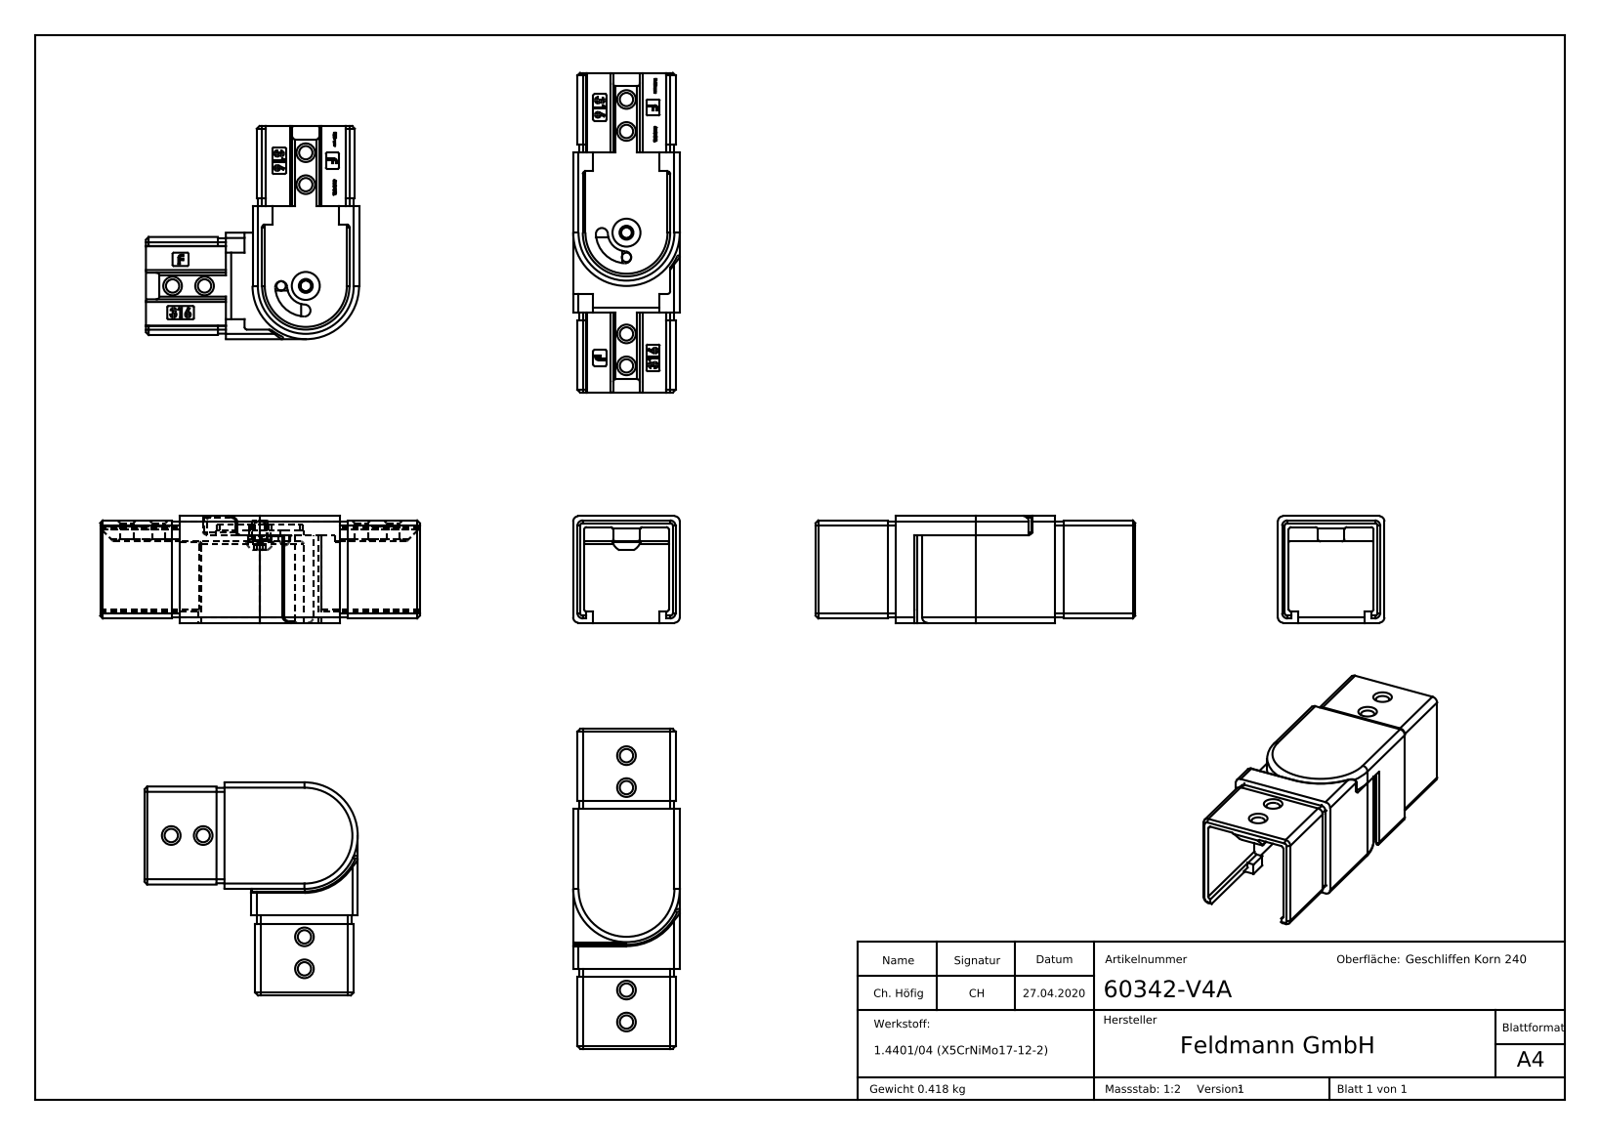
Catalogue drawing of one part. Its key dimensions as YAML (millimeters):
part_name: "60342-V4A; DIN 7380_DIN 7380 M6x8; 60342-V4A Teil2; 60342-V4A Teil2_60342-V4A Teil2 (+3 more)"
step_written_by: "SolidWorks 2015 (CONFIG_CONTROL_DESIGN)"
units: millimeters
bodies: {solids: 3, faces: 629, planar: 345, cylindrical: 104, other: 180}
overall_size: [120, 40.5, 40]
volume: 52291
surface_area: 34302
round_holes:
  - {diameter: 5, count: 5}
  - {diameter: 9, count: 1}
  - {diameter: 32.8, count: 1}
round_bosses_or_shafts:
  - {diameter: 40, count: 1}
  - {diameter: 10.5, count: 1}
  - {diameter: 8, count: 1}
  - {diameter: 6, count: 1}
  - {diameter: 3.5, count: 1}
partial_cylinders:
  - {radius: 1, count: 30}
  - {radius: 0.5, count: 20}
  - {radius: 2, count: 8}
  - {radius: 1.5, count: 4}
  - {radius: 2.25, count: 2}
  - {radius: 7, count: 1}
  - {radius: 11.5, count: 1}
  - {radius: 21, count: 1}
face_to_face_distances: [2.5, 1.6, 4.1, 34.3, 35.9, 38.4, 5.4, 2, 31.8, 0.5]
hole_center_spacings: [12, 38, 50, 88, 76, 100]
